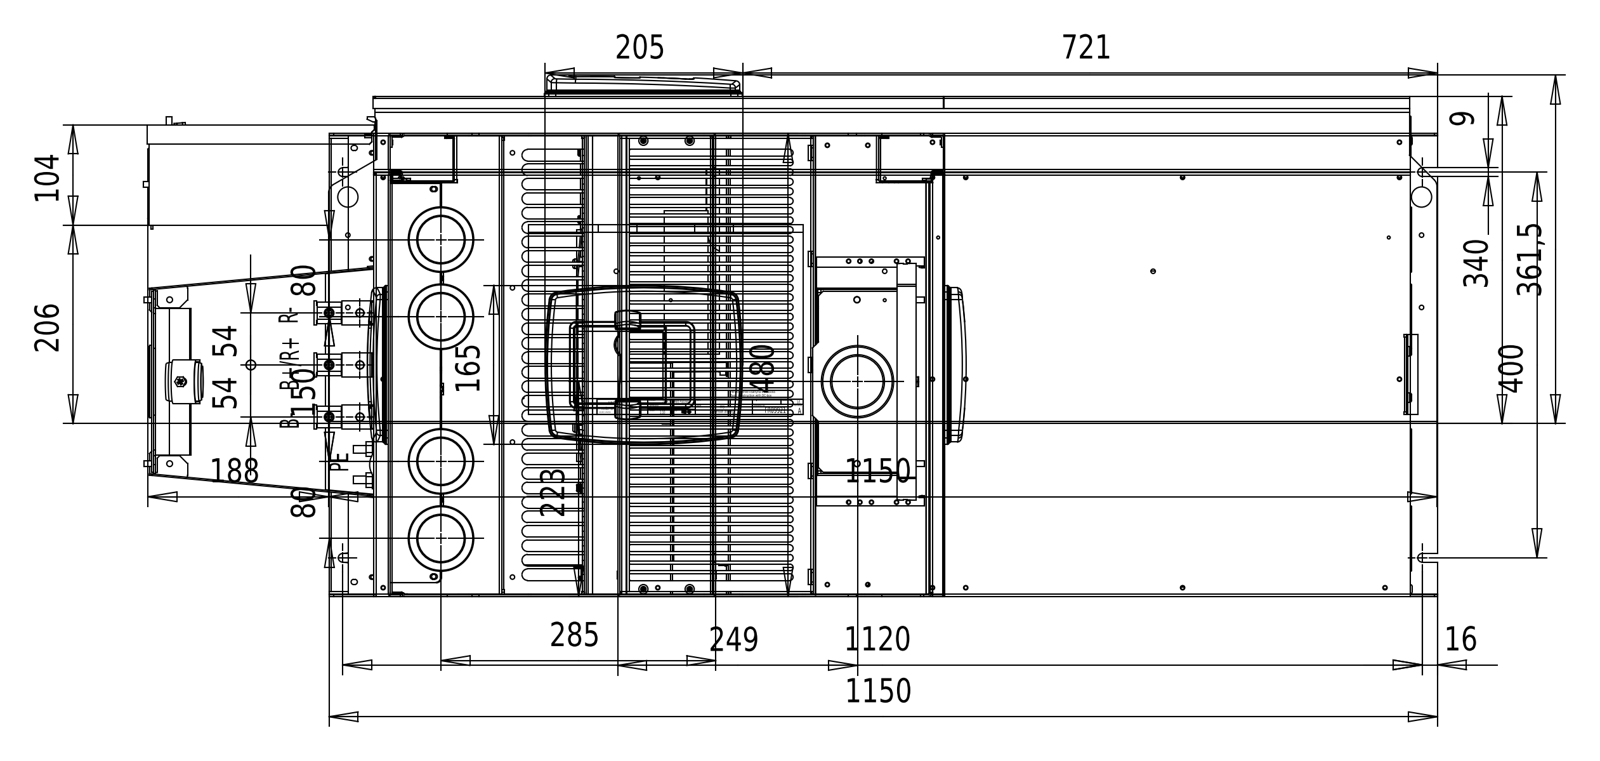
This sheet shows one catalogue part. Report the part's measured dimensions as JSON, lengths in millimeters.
{"part_name": "FR09_DC_COVER", "step_written_by": "CREO PARAMETRIC BY PTC INC, 2018070 (CONFIG_CONTROL_DESIGN)", "units": "millimeters", "bodies": {"solids": 15, "faces": 6783, "planar": 2819, "cylindrical": 3258, "other": 706}, "overall_size": [1342, 480.02, 362.03], "volume_mm3": 5166000, "surface_area_mm2": 7867000, "round_holes": [[3.6, 77], [4.5, 59], [4.6, 58], [3.3, 37], [3, 23], [5.5, 22], [2.5, 11], [4.3, 8], [5.2, 8], [6, 8], [77.8, 8], [16, 5]], "round_bosses_or_shafts": [[10, 31], [4, 30], [5, 20], [7.5, 17], [8, 16], [6, 15], [4.56, 9], [8.7, 8]], "partial_cylinders_radius": [[0.42, 222], [0.88, 222], [3.5, 171], [4, 94], [6, 75], [1, 65], [0.37, 64], [2, 62]], "face_to_face_distances": [2, 1.5, 478, 336, 338, 339.5, 337.5, 476, 480, 2.2], "hole_center_spacings": [44.1, 108, 90, 140.58, 465, 62.36, 38, 66.57]}
